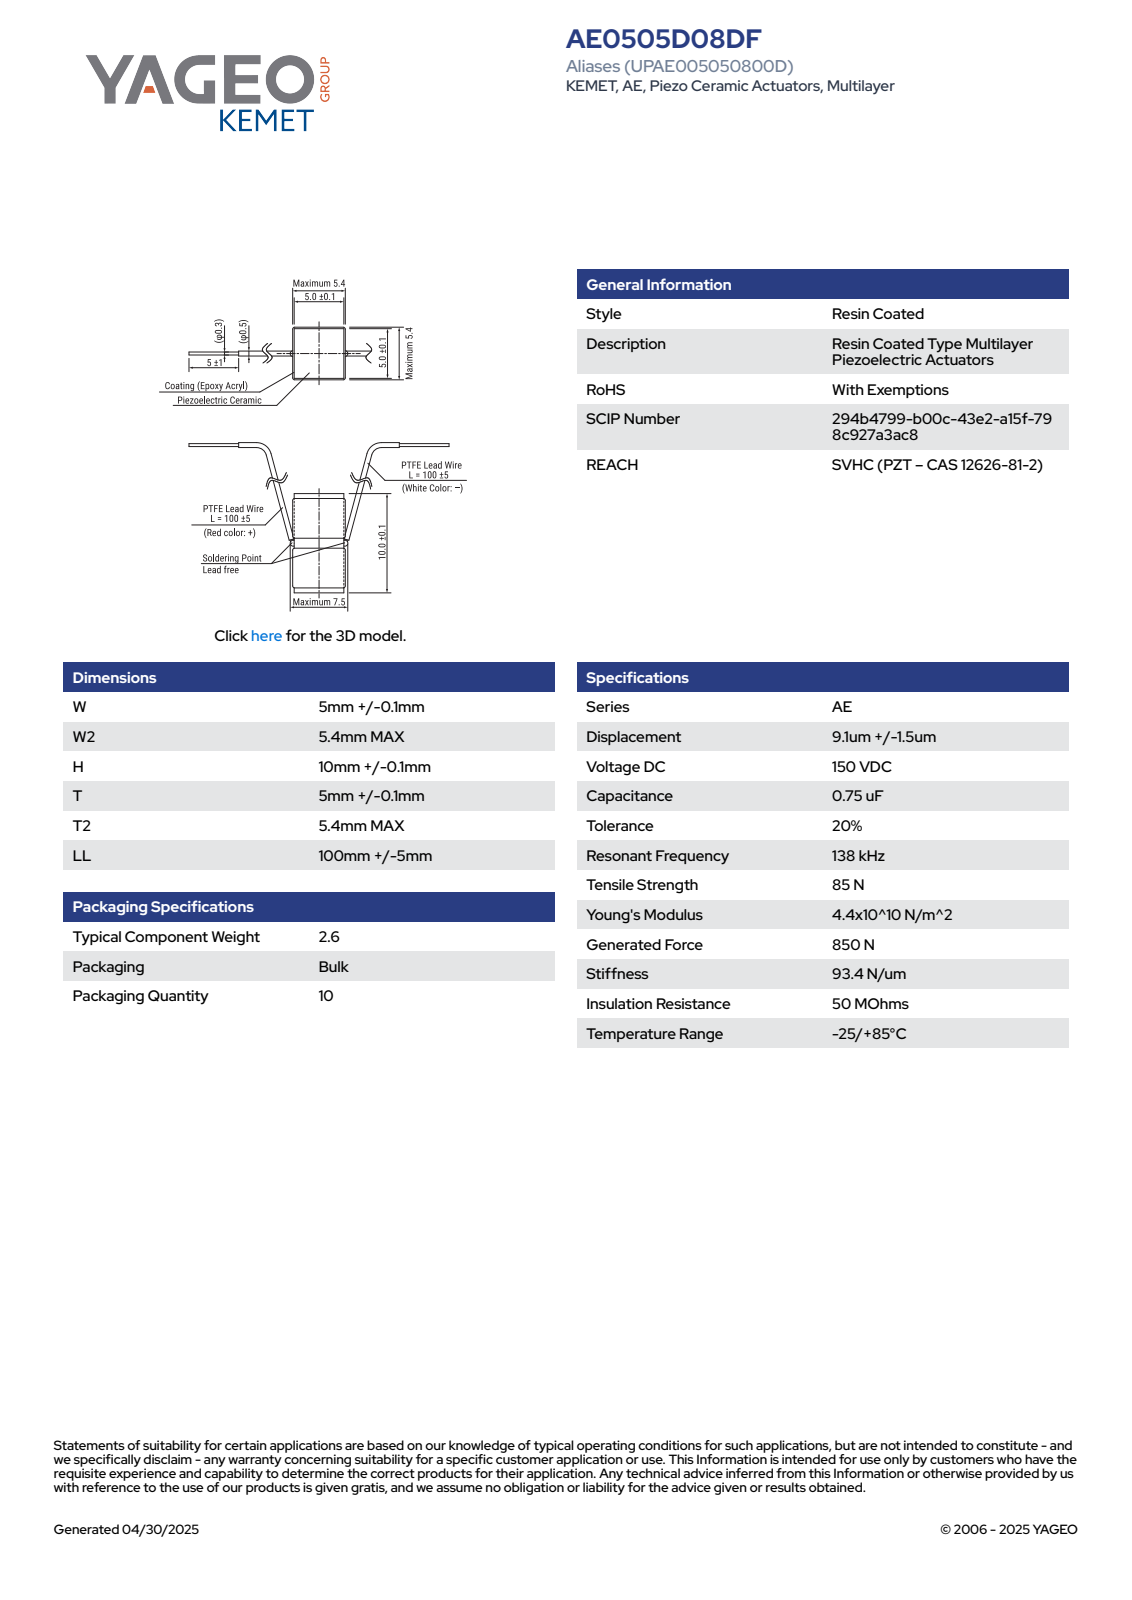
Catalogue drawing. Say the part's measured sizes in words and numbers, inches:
The part is named "AL_KAE1_W5.1W25.4H10.1T5.1T25.4". Its 3-D file was written by "SolidWorks 2014 (AUTOMOTIVE_DESIGN)". It is 4 solids with 93 faces: 85 planar, 8 cylindrical and 0 other. Overall it measures 0.398 by 0.213 by 0.213 inches. Its volume is 0.016 cubic inches and its surface area 0.426 square inches. Partial cylindrical surfaces (rounded edges, fillets, slot ends): 8 of radius 0.006. The main face-to-face distances are 0.201, 0.207, 0.197, 0.193, 0.398, 0.213, 0.16, 0.238, 0.039, 0.359.
